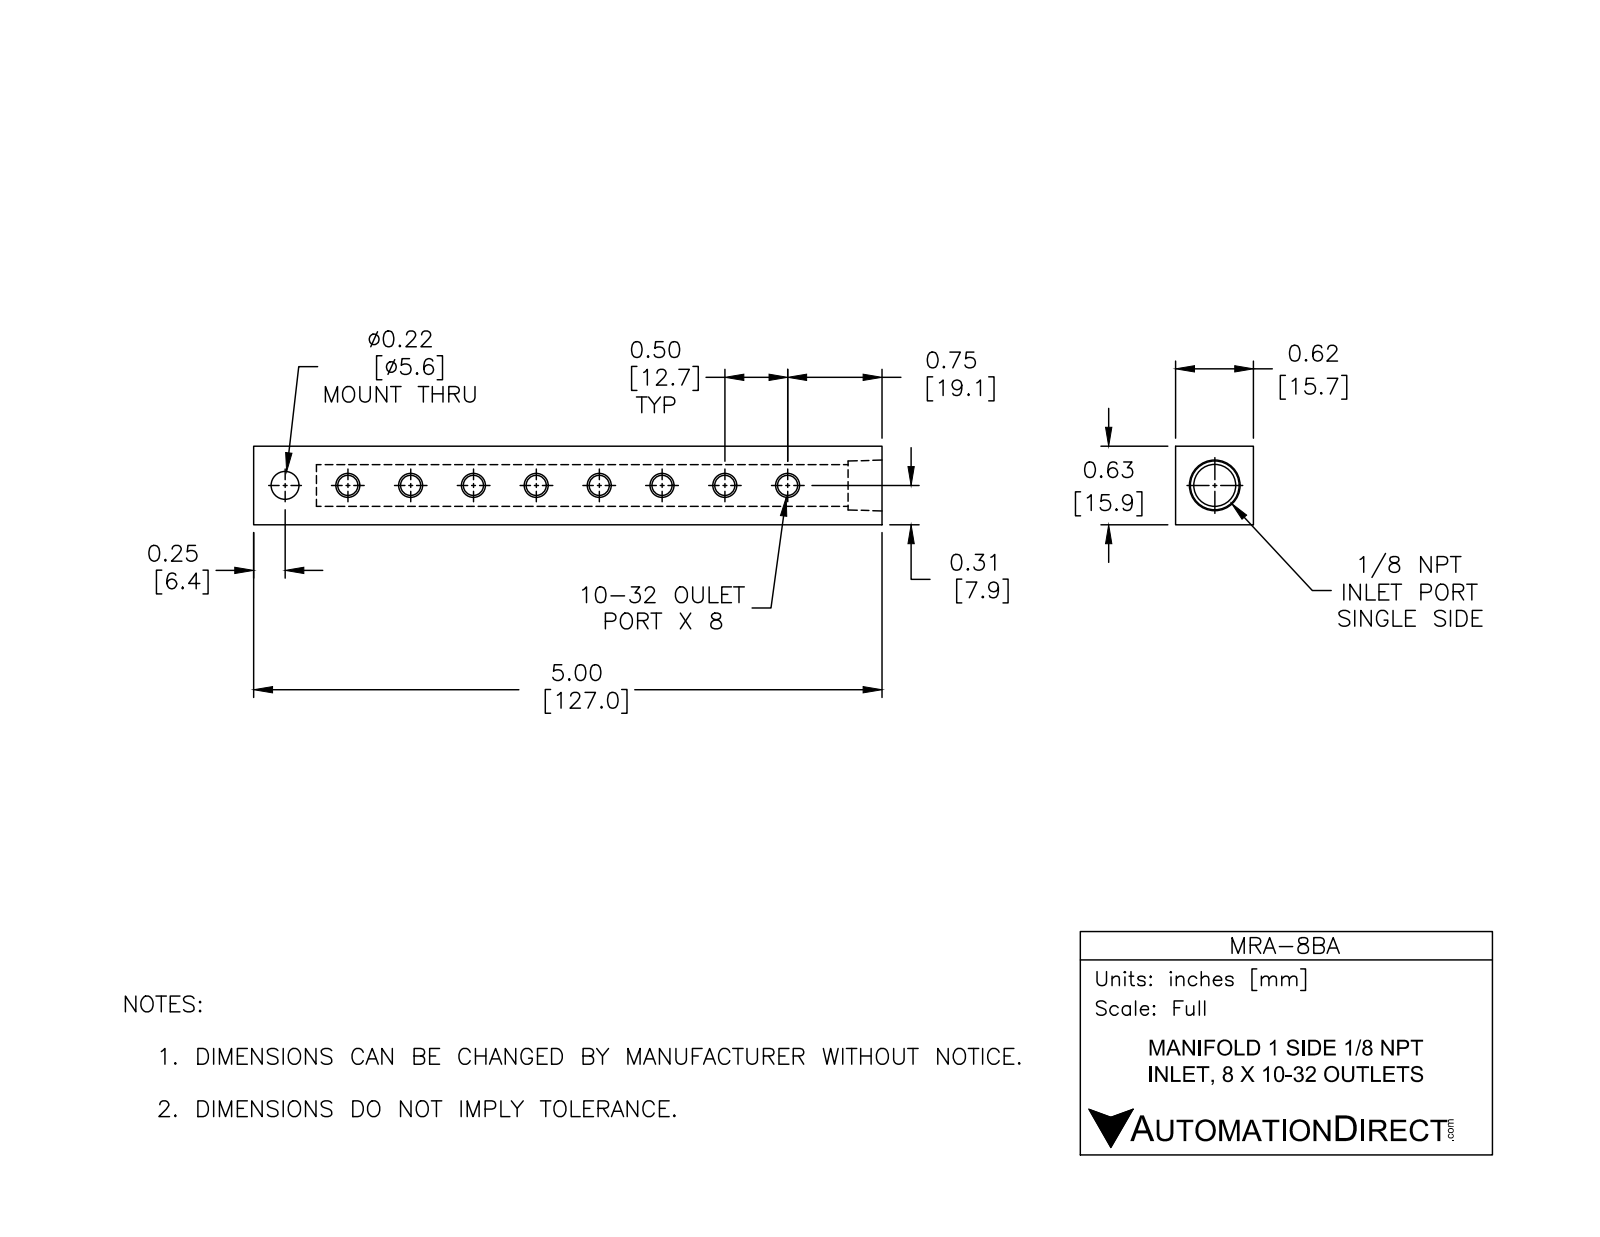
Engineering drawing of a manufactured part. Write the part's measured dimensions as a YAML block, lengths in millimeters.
part_name: "MRA-8BA"
step_written_by: "SolidWorks 2015 (CONFIG_CONTROL_DESIGN)"
units: millimeters
bodies: {solids: 1, faces: 30, planar: 8, cylindrical: 20, other: 2}
overall_size: [127, 15.9, 15.7]
volume: 24420
surface_area: 12010
round_holes:
  - {diameter: 4, count: 8}
  - {diameter: 5.6, count: 1}
  - {diameter: 8.4, count: 1}
face_to_face_distances: [15.9, 15.7, 127, 12.7, 114.3, 120.1, 107.4, 6.9]
hole_center_spacings: [12.7, 25.4, 38.1, 50.8, 63.5, 76.2, 88.9, 101.6]
